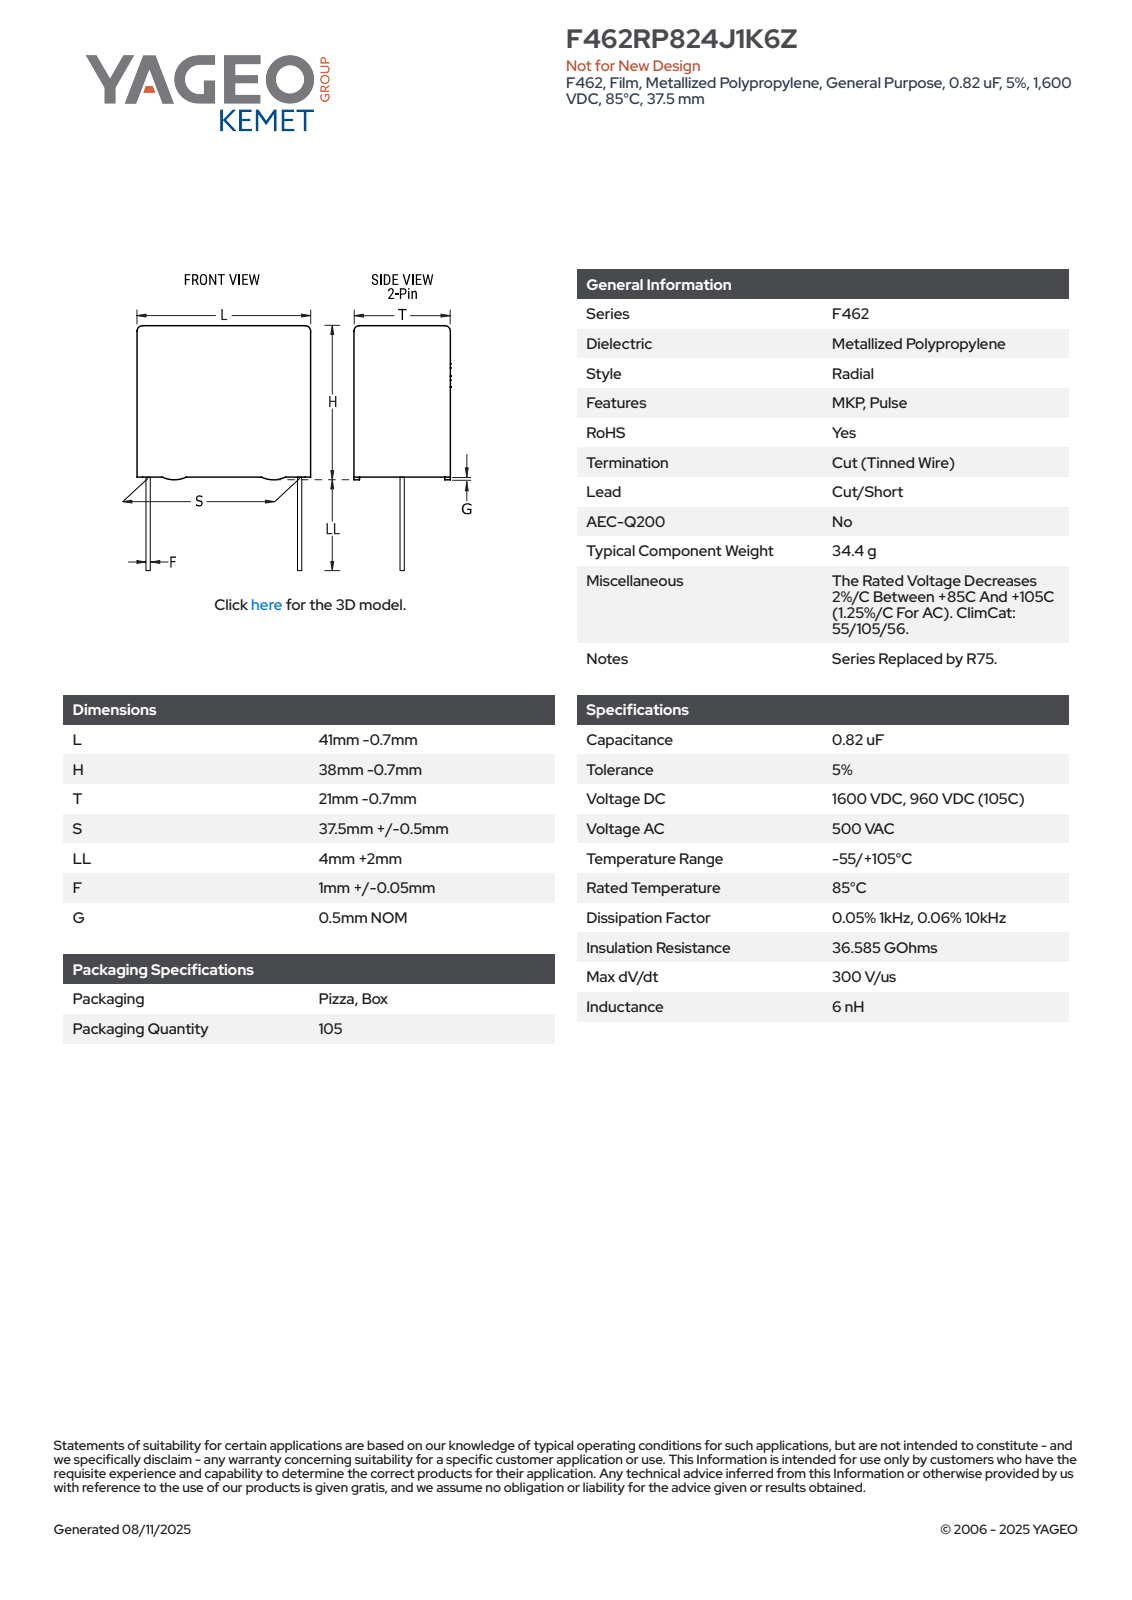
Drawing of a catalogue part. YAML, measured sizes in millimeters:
part_name: "CFR_RBG_41X38X21_L40.3H37.3T20.3S37.5LL6F1.05G0.5"
step_written_by: "SolidWorks 2014 (AUTOMOTIVE_DESIGN)"
units: millimeters
bodies: {solids: 4, faces: 89, planar: 81, cylindrical: 8, other: 0}
overall_size: [43.3, 40.3, 20.3]
volume: 30126
surface_area: 6317
round_bosses_or_shafts:
  - {diameter: 1.05, count: 2}
partial_cylinders:
  - {radius: 0.5, count: 4}
face_to_face_distances: [20.3, 36.8, 40.3, 20.31, 0.5, 37.3, 1.16, 19.14, 1.17, 17.98]
